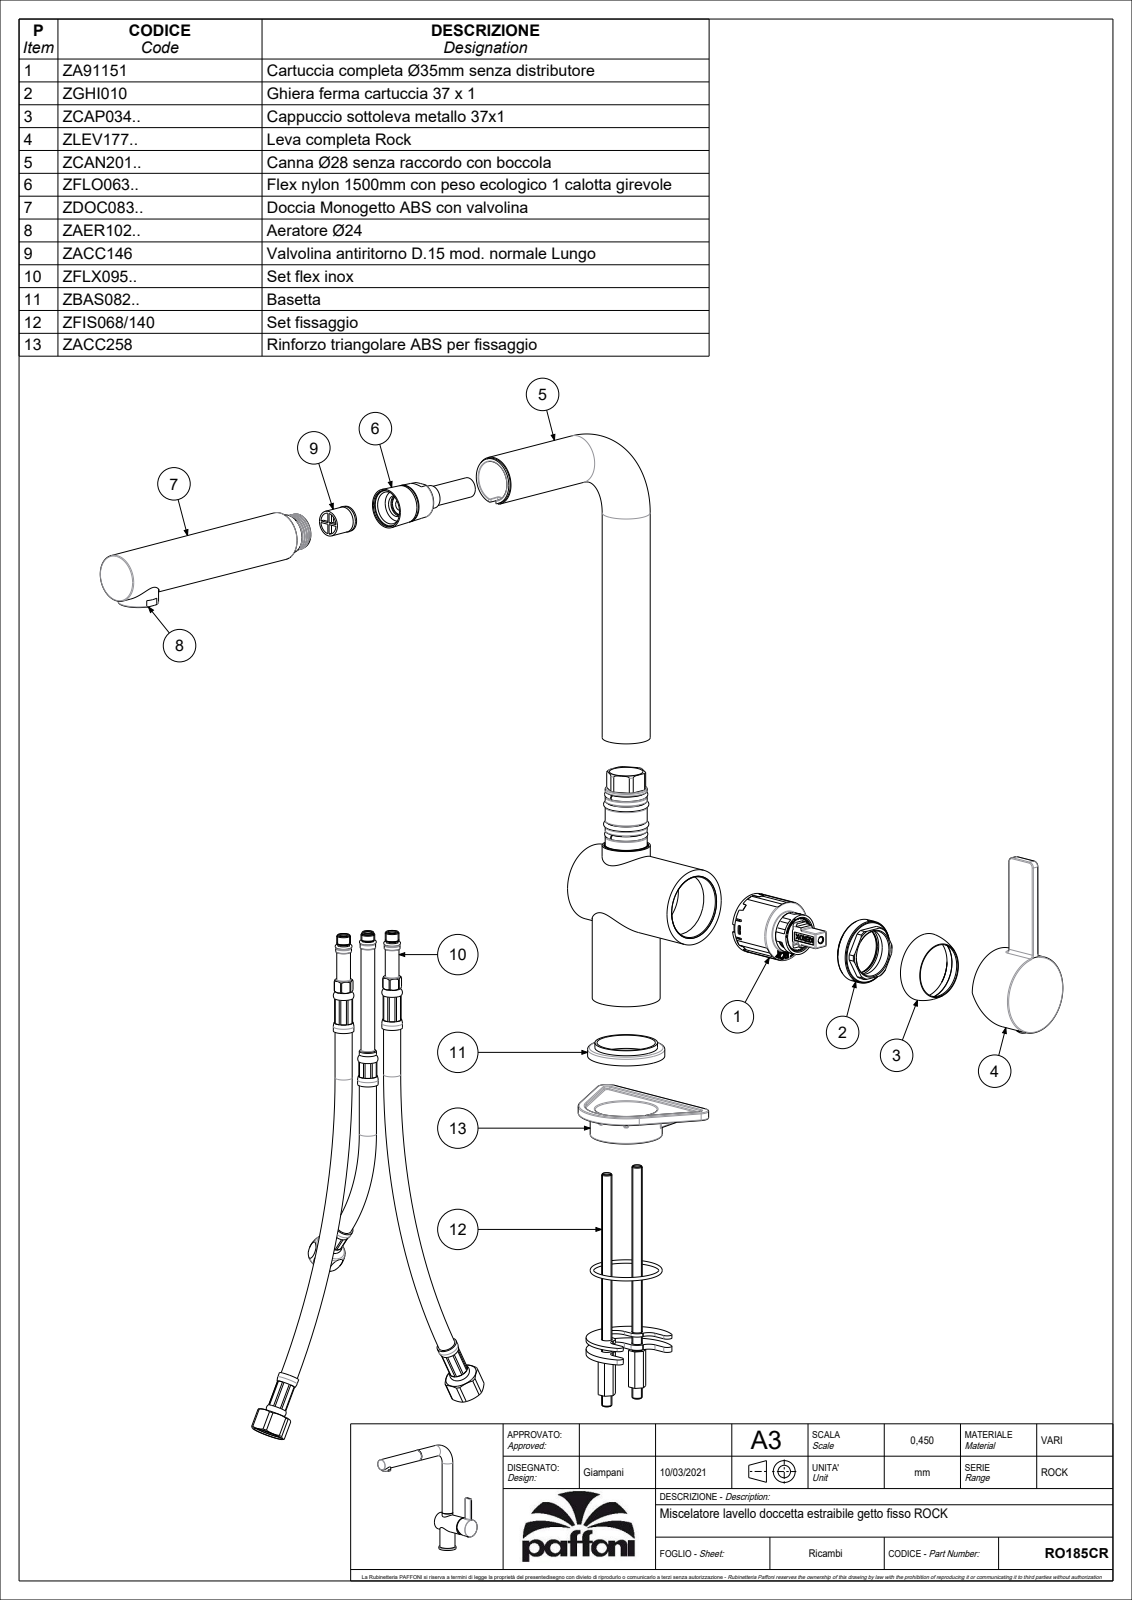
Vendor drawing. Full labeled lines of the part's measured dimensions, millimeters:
Part name (STEP PRODUCT): RO185CR
STEP written by: CREO PARAMETRIC BY PTC INC, 2020044 (CONFIG_CONTROL_DESIGN)
Units: millimetres
Bodies: 0 solids, 116 faces (32 planar, 41 cylindrical, 43 other)
Overall size (bounding box): 286.7 × 269.75 × 114.1
Round holes (diameter × count): ⌀25 ×1
Round bosses / shafts (diameter × count): ⌀28 ×2, ⌀45.5 ×1, ⌀45 ×1, ⌀44.7 ×1, ⌀39.6 ×1, ⌀26.8 ×1, ⌀23.5 ×1, ⌀22.7 ×1
Partial cylindrical surfaces — rounded edges, fillets, slot ends (radius × count): R0.5 ×6, R1 ×2, R2 ×2, R3 ×2, R12.2 ×1, R13.8 ×1
Main face-to-face distances: 82, 5, 4.5, 113.25, 108.75, 7.5, 105.75, 101.25, 254.7, 249.7
